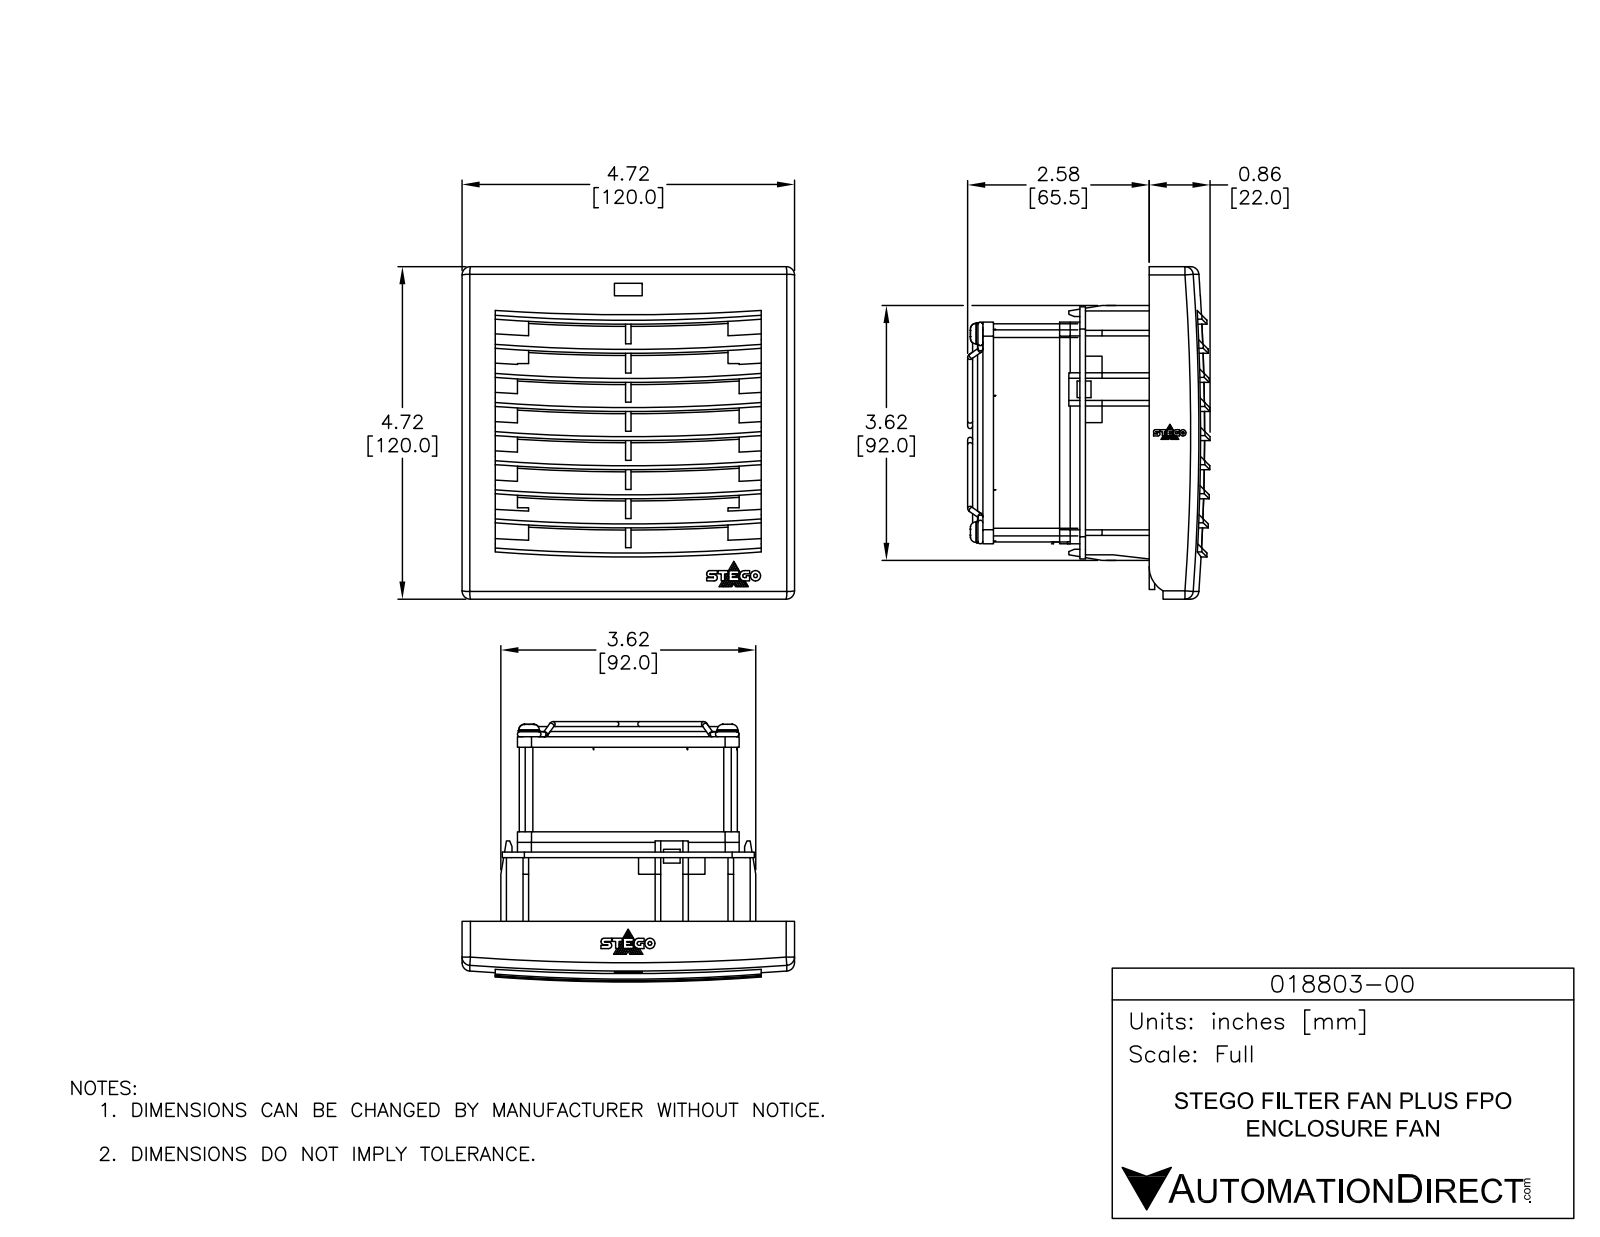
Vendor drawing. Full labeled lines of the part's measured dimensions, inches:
Part name (STEP PRODUCT): 018803-00
STEP written by: SolidWorks 2018 (AUTOMOTIVE_DESIGN)
Units: inches
Bodies: 1 solid, 506 faces (293 planar, 205 cylindrical, 8 other)
Overall size (bounding box): 4.724 × 4.724 × 3.74
Volume: 20.27 in³ · Surface area: 222.5 in²
Round holes (diameter × count): ⌀0.217 ×4, ⌀0.671 ×1, ⌀1.153 ×1, ⌀1.635 ×1, ⌀1.996 ×1, ⌀2.117 ×1, ⌀2.496 ×1, ⌀2.677 ×1, ⌀3.079 ×1
Round bosses / shafts (diameter × count): ⌀2.661 ×1, ⌀2.274 ×1, ⌀2.161 ×1, ⌀1.792 ×1, ⌀1.31 ×1, ⌀0.937 ×1, ⌀0.828 ×1
Partial cylindrical surfaces — rounded edges, fillets, slot ends (radius × count): R8.63 ×15, R1.312 ×5, R0.1 ×4, R0.118 ×4, R0.539 ×1, R0.748 ×1, R0.83 ×1, R1.715 ×1
Main face-to-face distances: 0.059, 0.316, 0.12, 0.091, 3.531, 0.632, 0.239, 0.375, 0.551, 0.642
Hole centre spacings: 2.082, 2.945, 4.165
